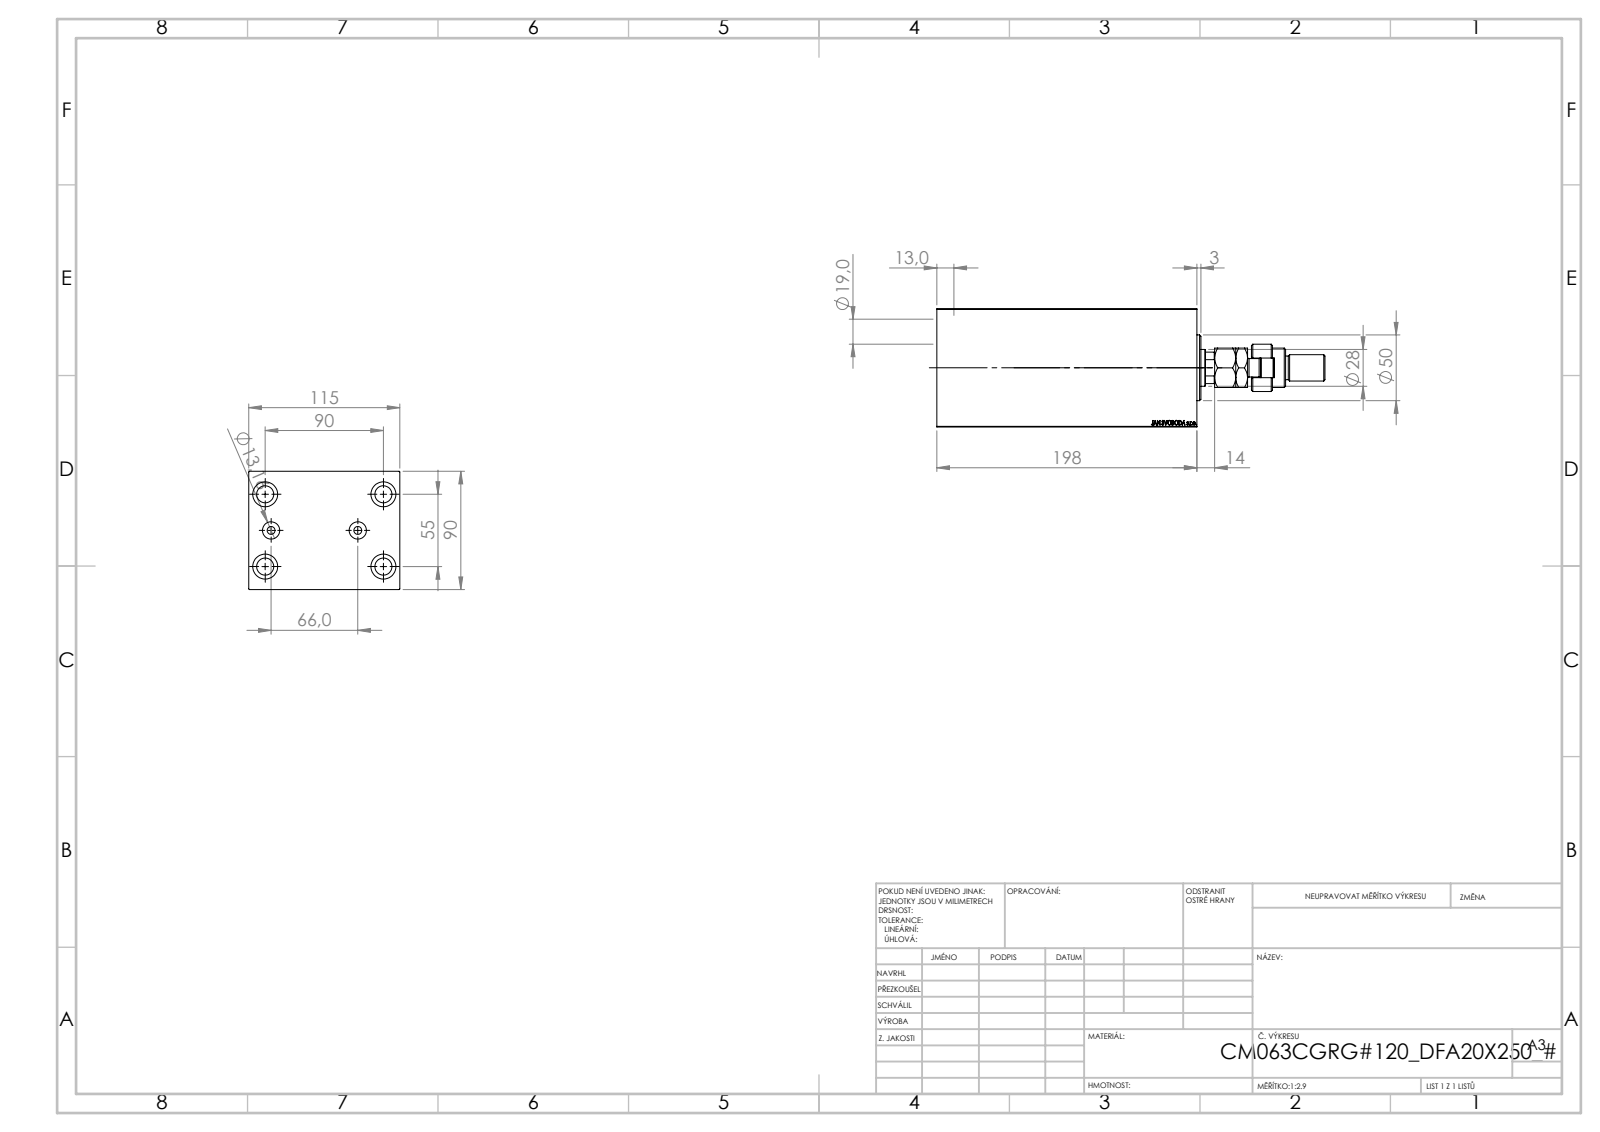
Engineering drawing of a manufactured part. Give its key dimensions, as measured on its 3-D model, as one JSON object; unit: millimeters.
{"part_name": "V450CM_VC_B; V450CM_C_VCP; MFA; V450CM_C_Body (+1 more)", "step_written_by": "SolidWorks 2019 (CONFIG_CONTROL_DESIGN)", "units": "millimeters", "bodies": {"solids": 5, "faces": 946, "planar": 437, "cylindrical": 71, "other": 438}, "overall_size": [295.5, 115, 90], "volume_mm3": 1670000, "surface_area_mm2": 232131, "round_holes": [[13, 4], [19, 4], [6, 2], [13.16, 2], [18.5, 1], [28, 1], [31.5, 1], [63, 1], [65, 1], [72, 1]], "round_bosses_or_shafts": [[50, 1], [36, 1], [30, 1], [22, 1], [20, 1], [18, 1], [14, 1]], "partial_cylinders_radius": [[7.5, 1], [12, 1], [13.5, 1]], "face_to_face_distances": [90, 115, 198, 17.5, 180.5, 29.3, 151.2, 168.7, 149.3, 120], "hole_center_spacings": [30, 52.74, 82.71, 33, 55, 90, 105.48, 66]}
